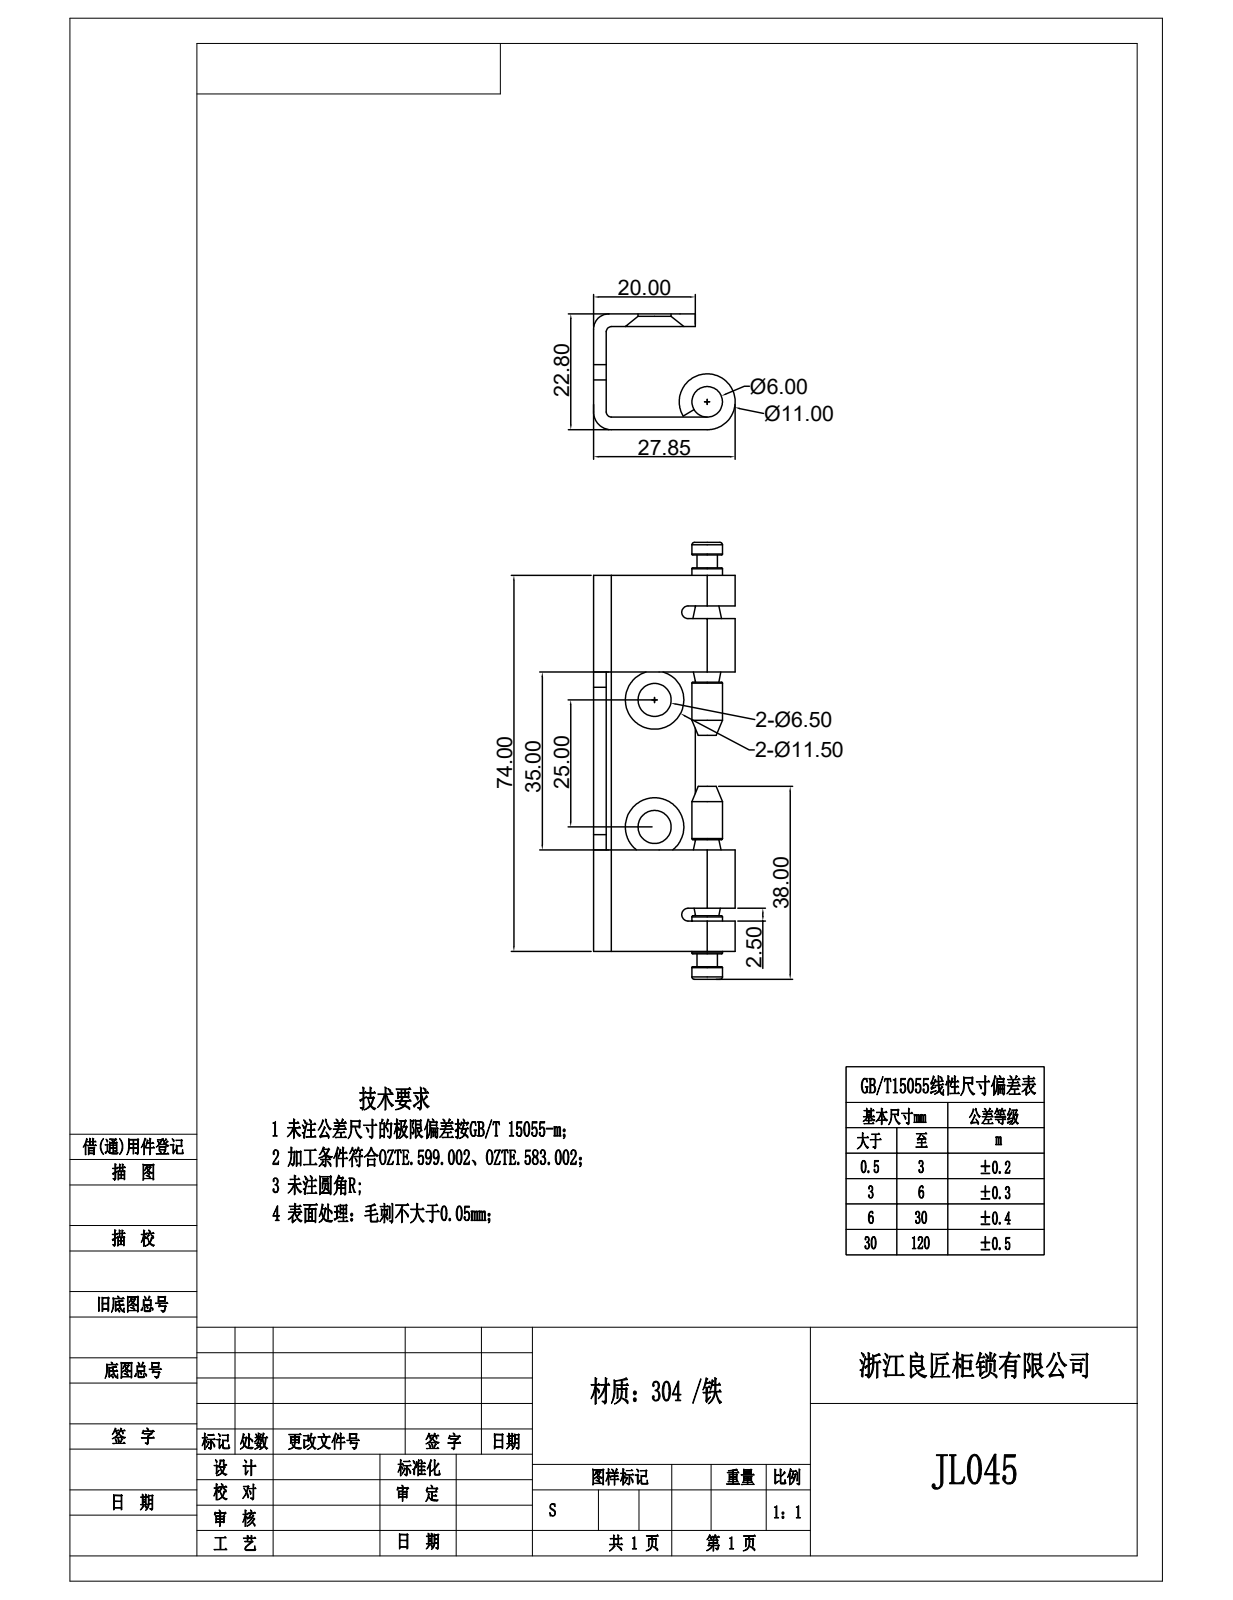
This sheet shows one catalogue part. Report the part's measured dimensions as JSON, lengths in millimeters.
{"step_written_by": "Rhino 8.5 (CONFIG_CONTROL_DESIGN)", "units": "millimeters", "bodies": {"solids": 3, "faces": 124, "planar": 44, "cylindrical": 44, "other": 36}, "overall_size": [86, 27.85, 22.8], "volume_mm3": 11511, "surface_area_mm2": 10632, "round_holes": [[6.5, 2]], "round_bosses_or_shafts": [[11, 1], [6, 1], [4, 1]], "partial_cylinders_radius": [[3, 5], [1, 2], [1.25, 2], [3.5, 1]], "face_to_face_distances": [2.5, 20.3, 22.8, 17.8, 20, 74, 17.5, 6, 68, 8.5], "hole_center_spacings": [25]}
